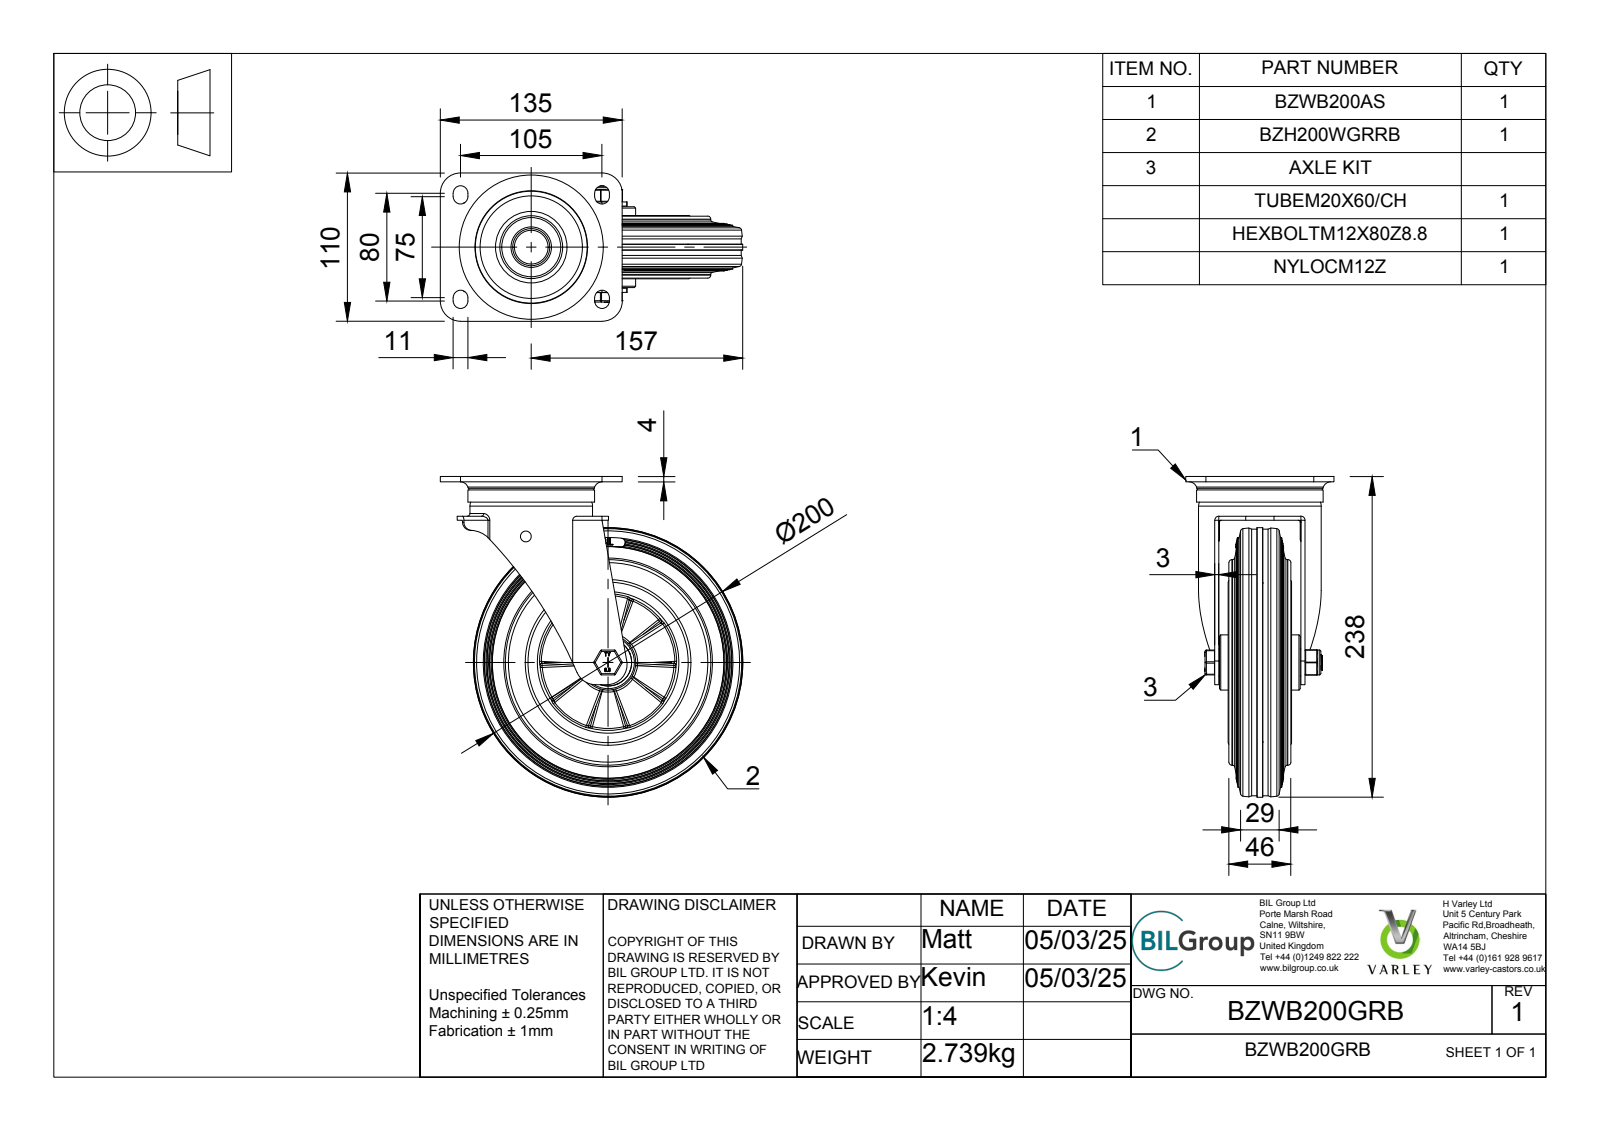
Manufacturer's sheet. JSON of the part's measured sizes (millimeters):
{"part_name": "BZWB200GRB v3; BZWB200AS v1; ZINC PLATED, PRESSED STEEL TOP PLATE; ZINC PLATED, PRESSED STEEL FORKS (+7 more)", "step_written_by": "Autodesk Translation Framework v13.20.0.188 (AP242_MANAGED_MODEL_BASED_3D_ENGINEERING_MIM_LF)", "units": "millimeters", "bodies": {"solids": 19, "faces": 812, "planar": 216, "cylindrical": 188, "other": 408}, "overall_size": [238, 224.5, 110], "volume_mm3": 1182000, "surface_area_mm2": 302784, "round_holes": [[8, 1], [12, 1], [12.2, 1], [12.5, 1], [14, 1], [20, 1], [35, 1], [55, 1], [85, 1], [93, 1], [101, 1], [118, 1]], "round_bosses_or_shafts": [[7.5, 8], [197.81, 1], [152.5, 1], [123, 1], [94, 1], [91, 1], [63, 1], [41, 1]], "partial_cylinders_radius": [[0.5, 18], [1, 12], [1.5, 8], [5.5, 8], [15, 6], [3, 4], [2, 2], [0.25, 1]], "face_to_face_distances": [3, 14.5, 49.5, 11.5, 4, 64, 10, 52.5, 2, 46.5], "hole_center_spacings": [111.64]}
